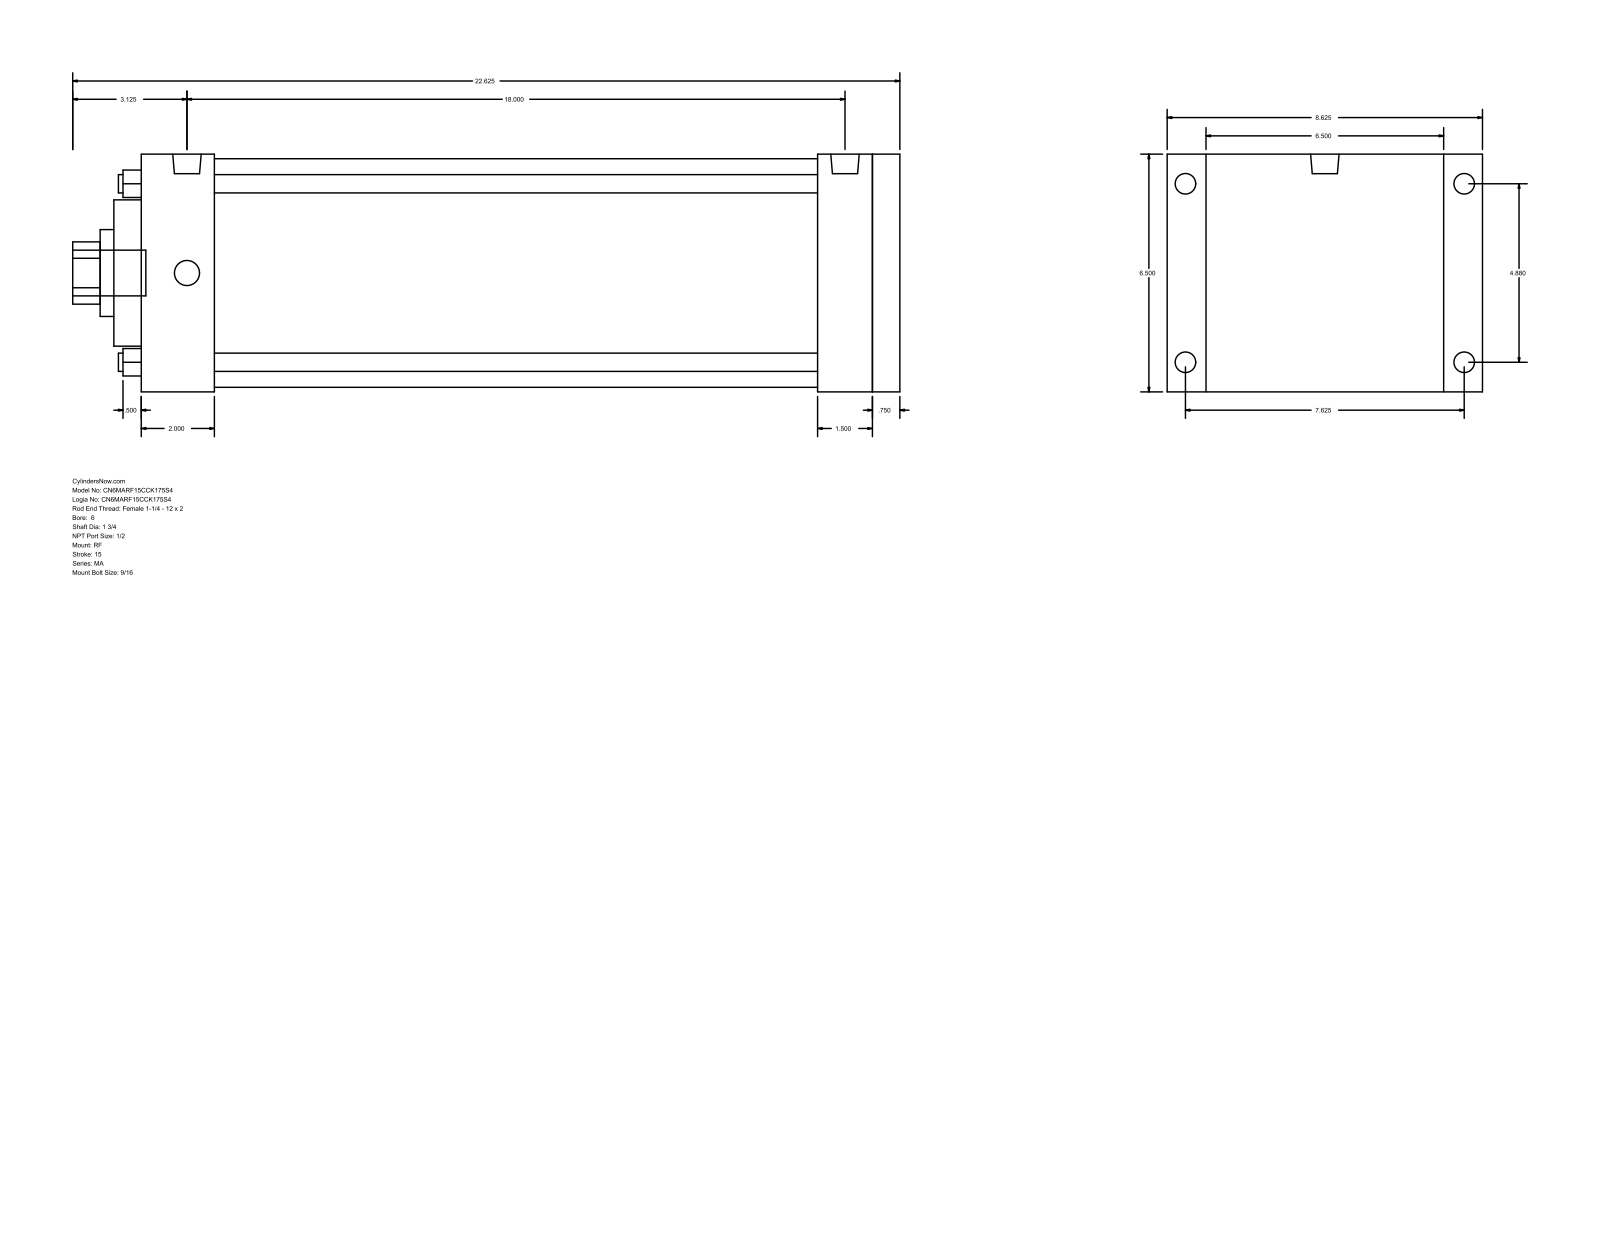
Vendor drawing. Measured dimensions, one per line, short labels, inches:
name: MA_RF__0600_1.75
written by: GSSL Pune (CONFIG_CONTROL_DESIGN)
unit: in
bodies: 0 solids, 94 faces (65 planar, 29 cylindrical, 0 other)
size: 22.625 × 8.625 × 6.5
holes: 4× ⌀0.5, 1× ⌀1.75, 1× ⌀2.375, 1× ⌀4, 1× ⌀6.25
bosses: 4× ⌀0.687, 4× ⌀0.563, 2× ⌀0.778, 1× ⌀1.25
rounds: 1× R0.852
face distances: 6.5, 20.75, 0.75, 20, 1.5, 2, 18, 18.75, 18.5, 16.5
hole spacings: 3.451, 4.88, 6.902
